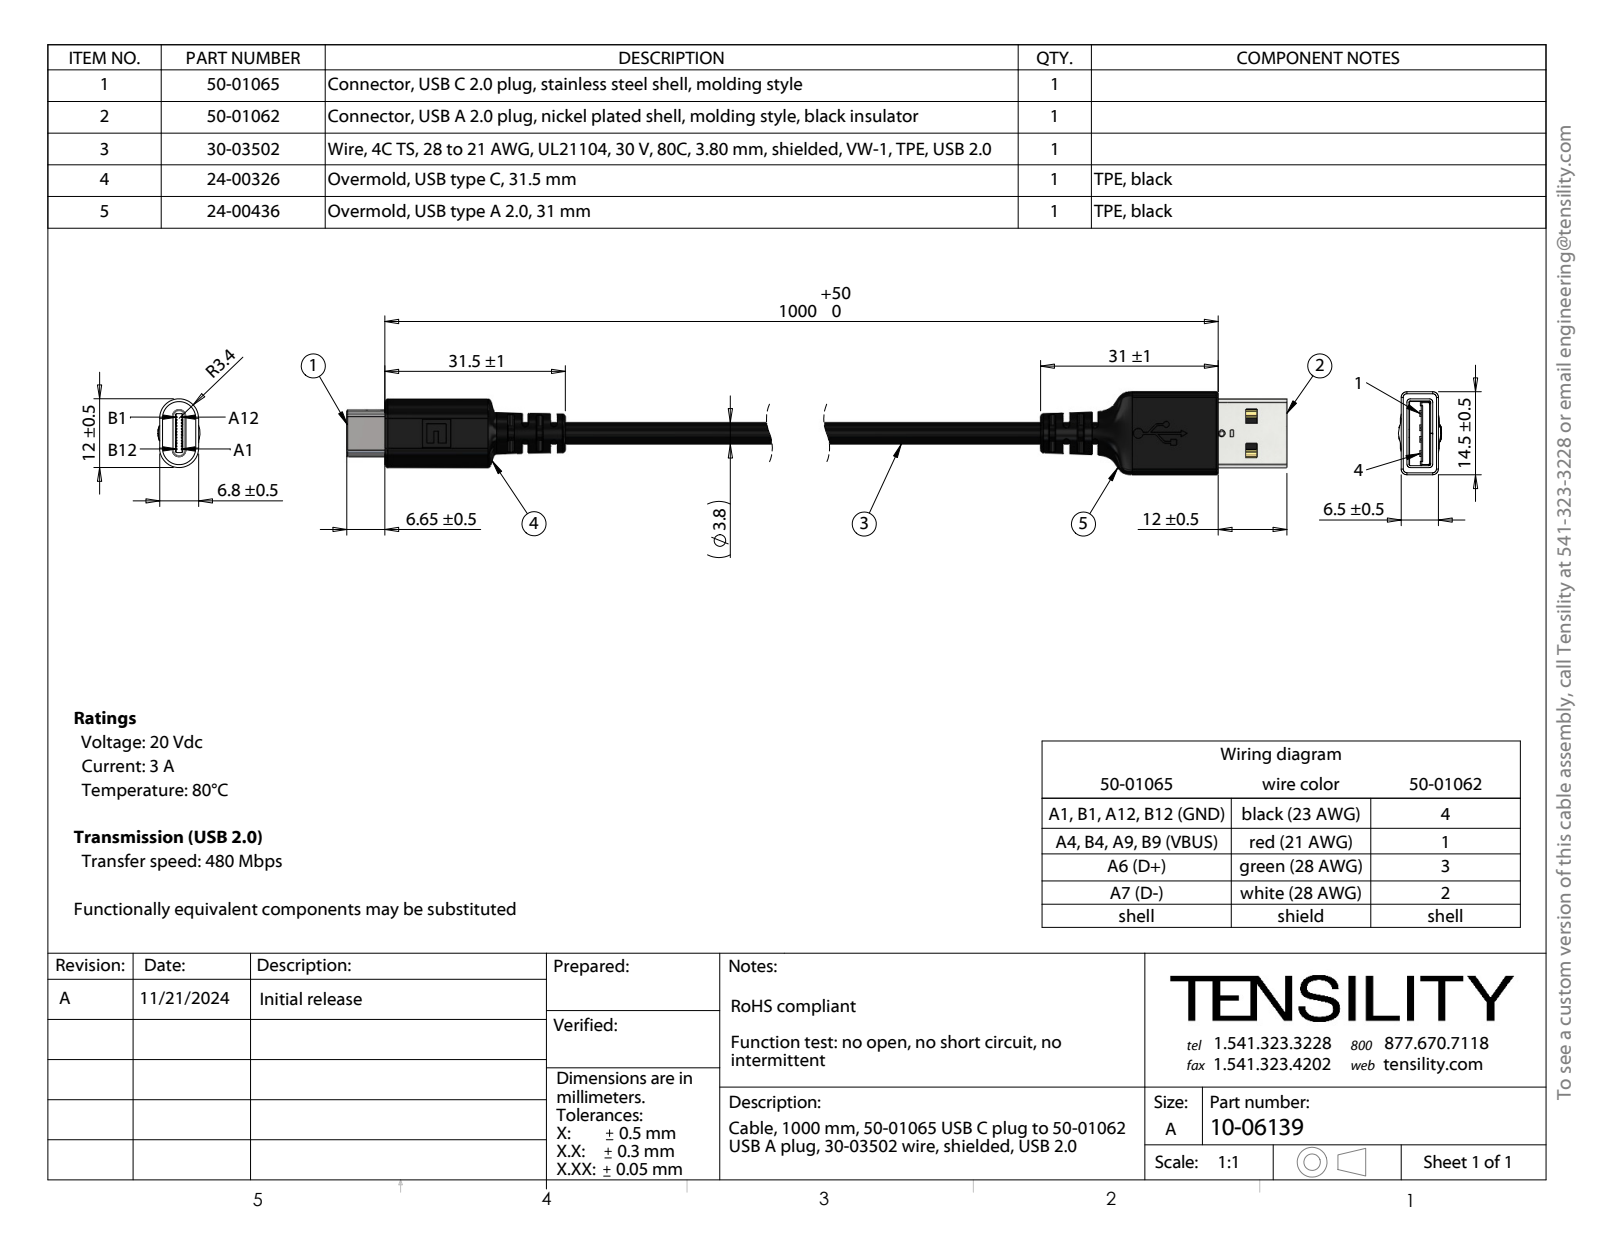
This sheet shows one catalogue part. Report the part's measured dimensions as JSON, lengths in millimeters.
{"part_name": "50-01062_insulator_model; 50-01062_crimp_Assembled; 50-01062_shell2; 24-00436 (+8 more)", "step_written_by": "SolidWorks 2021 (CONFIG_CONTROL_DESIGN)", "units": "millimeters", "bodies": {"solids": 125, "faces": 1970, "planar": 1014, "cylindrical": 630, "other": 326}, "overall_size": [200.15, 14.5, 7.54], "volume_mm3": 5918, "surface_area_mm2": 22580, "round_holes": [[1.04, 1], [1.74, 1], [2.61, 1], [2.64, 1], [2.84, 1]], "round_bosses_or_shafts": [[0.83, 2], [3.8, 1], [2.63, 1], [1.2, 1], [1, 1]], "partial_cylinders_radius": [[0.25, 40], [0.2, 34], [0.5, 32], [0.35, 14], [0.4, 14], [0.3, 13], [0.31, 5], [0.6, 5]], "face_to_face_distances": [0.35, 4.15, 1, 5.5, 1.35, 5.15, 1.5, 2.5, 4.5, 3.8], "hole_center_spacings": [5.13]}
